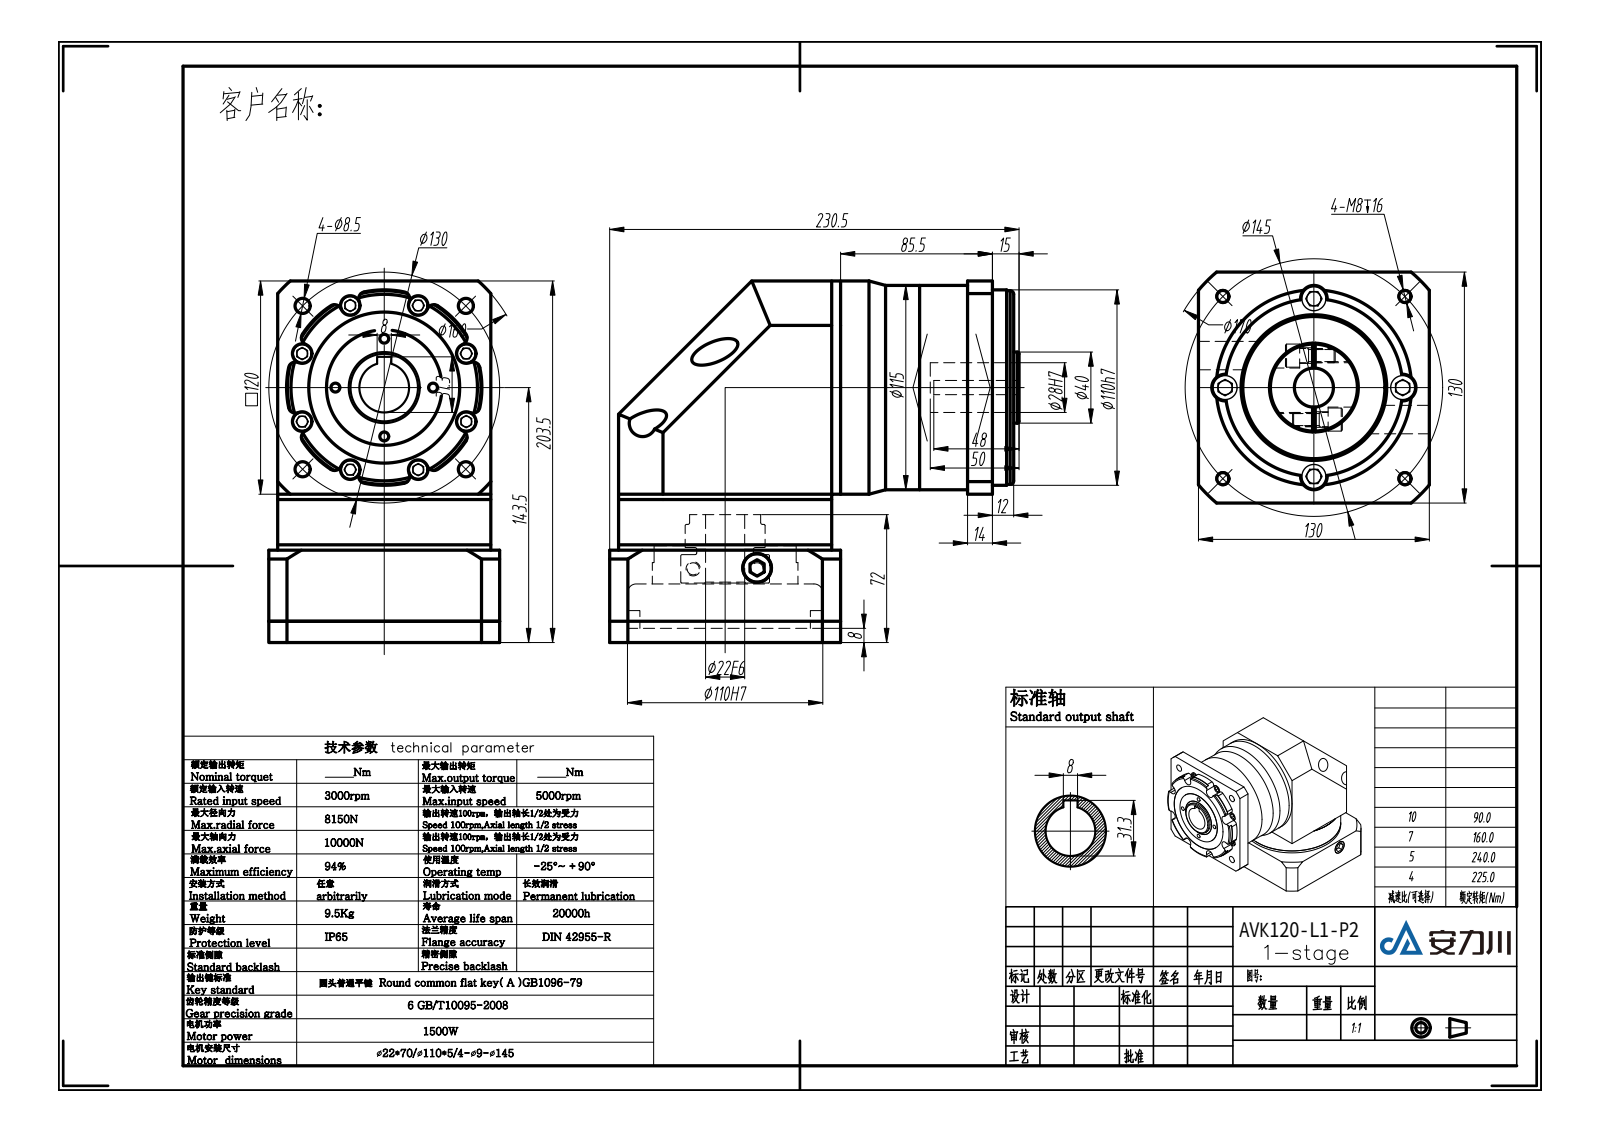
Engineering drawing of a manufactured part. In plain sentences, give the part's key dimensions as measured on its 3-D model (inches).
The part is named "VGE115后过渡板（-70 110-5 4-9-145）; VGZK115单级模型（22-70 110-5 4-9-145）; VGZK115单级模型". Its 3-D file was written by "SolidWorks 2016 (AUTOMOTIVE_DESIGN)". It is 23 solids with 523 faces: 277 planar, 217 cylindrical and 29 other. Overall it measures 9.075 by 8.012 by 5.118 inches. Its volume is 192.7 cubic inches and its surface area 585.9 square inches. Round holes: 8 of diameter 0.433, 6 of diameter 0.591, 4 of diameter 0.197, 4 of diameter 0.268, 4 of diameter 0.335, 4 of diameter 0.354, 2 of diameter 0.63, 1 of diameter 0.787, 1 of diameter 0.866, 1 of diameter 1.102, 1 of diameter 1.78, 1 of diameter 3.15. Round bosses or shafts: 10 of diameter 0.512, 8 of diameter 0.374, 2 of diameter 4.724, 2 of diameter 0.614, 1 of diameter 4.528, 1 of diameter 2.559, 1 of diameter 1.969, 1 of diameter 1.772. Partial cylindrical surfaces (rounded edges, fillets, slot ends): 16 of radius 0.157, 4 of radius 0.295, 1 of radius 2.146, 1 of radius 2.165, 1 of radius 3.15, 1 of radius 3.346. The main face-to-face distances are 0.197, 1.004, 1.949, 0.755, 1.752, 0.997, 1.194, 4.921, 4.724, 1.693. The hole center spacings are 2.854, 3.728, 1.507, 2.784, 3.637, 4.442, 0.098, 1.056.
